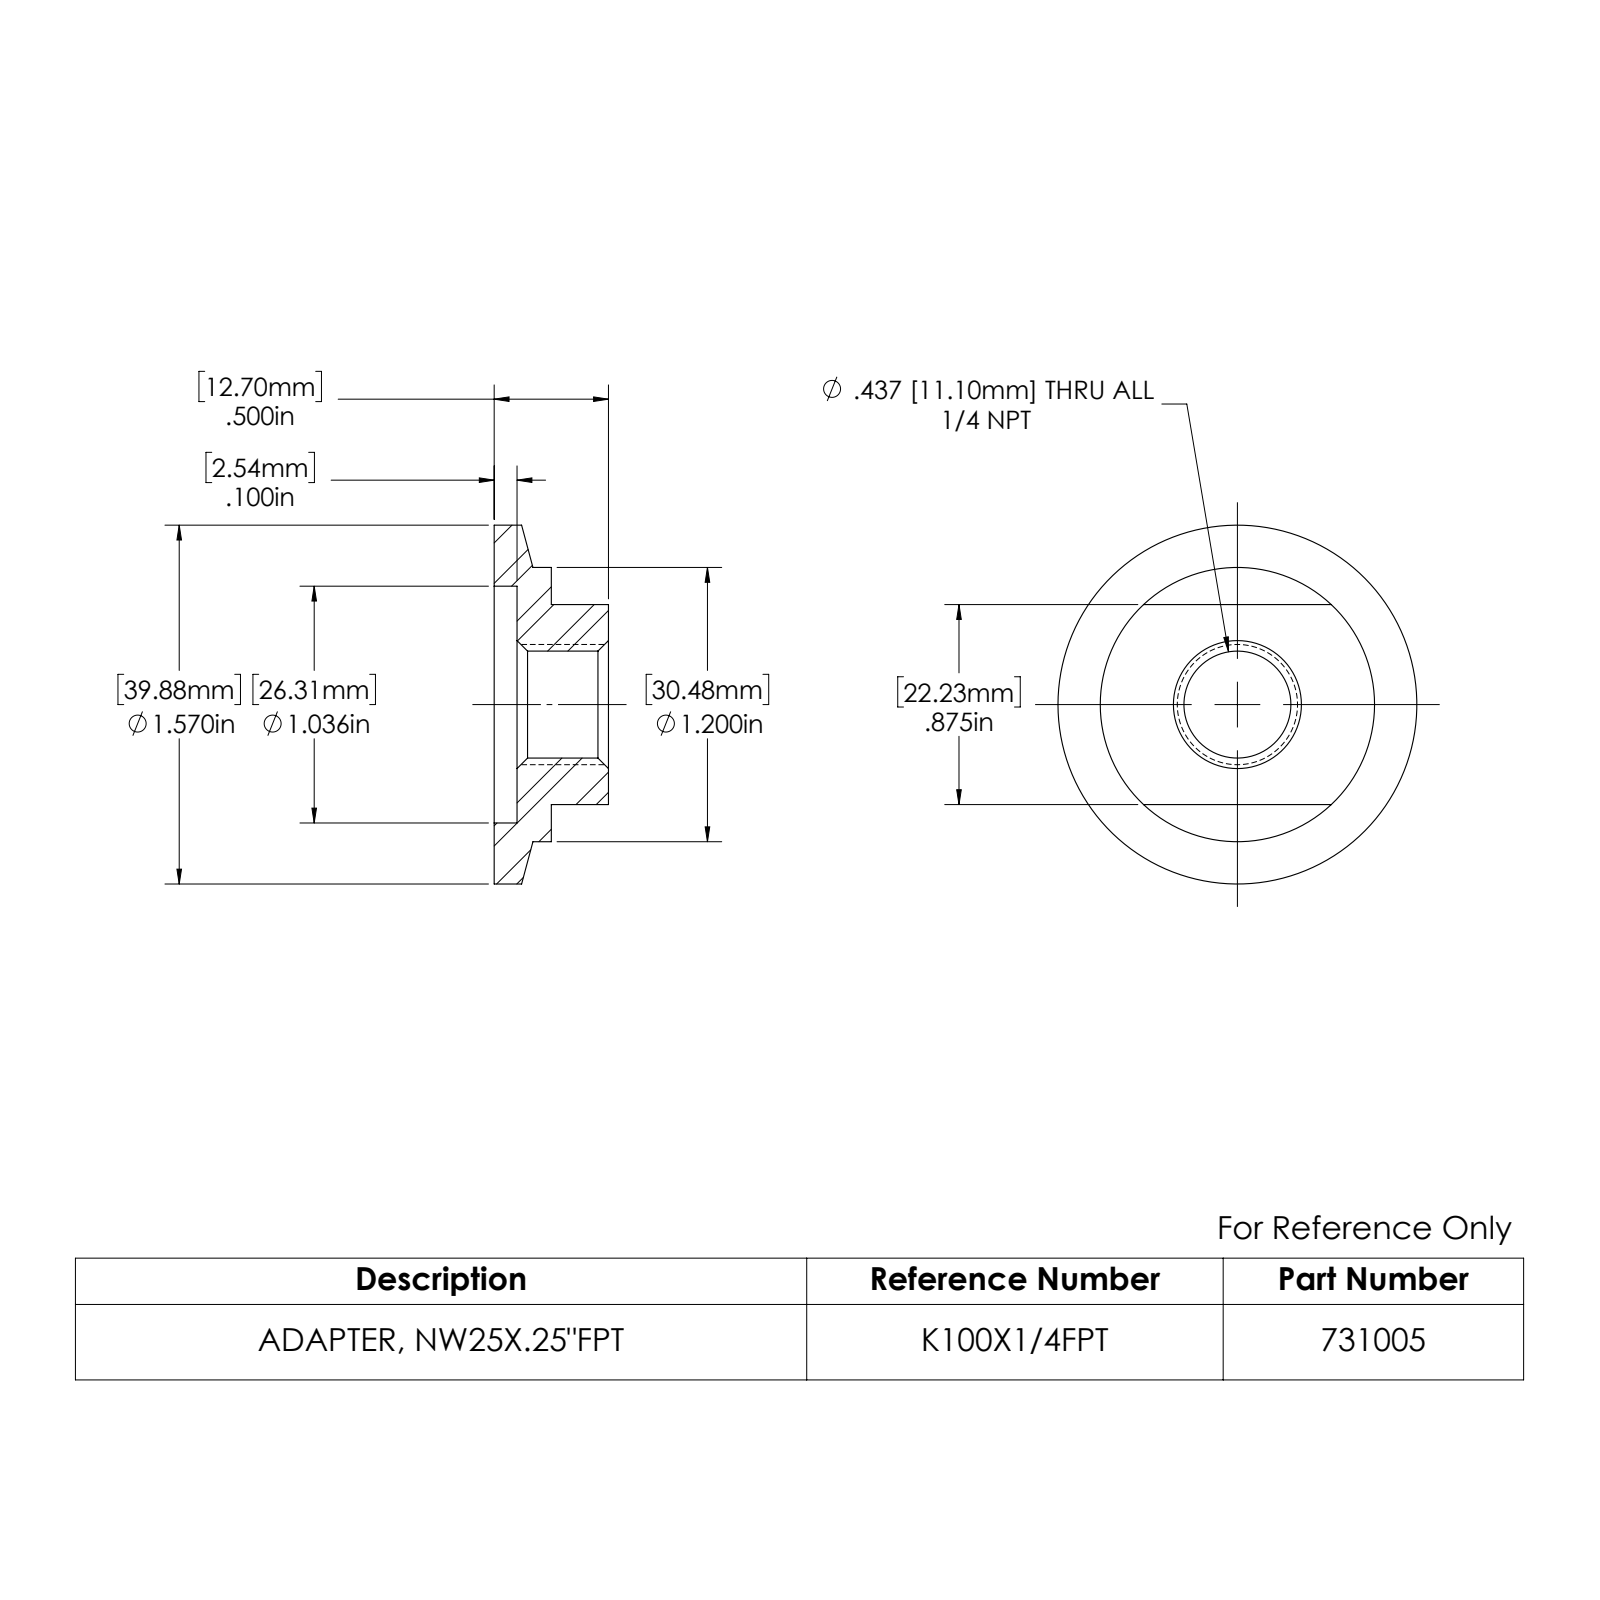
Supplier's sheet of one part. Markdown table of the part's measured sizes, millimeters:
| quantity | value |
| --- | --- |
| part name | 731005 |
| STEP written by | SolidWorks 2022 (AUTOMOTIVE_DESIGN) |
| units | millimeters |
| bodies | 1 solid, 21 faces (7 planar, 8 cylindrical, 6 other) |
| overall size | 39.9 × 39.9 × 12.7 |
| volume | 7 850 mm³ |
| surface area | 3 995 mm² |
| round holes (diameter × count) | 11.9 × 1, 26.3 × 1 |
| round bosses / shafts (diameter × count) | 39.9 × 1, 30.5 × 1 |
| main face-to-face distances | 12.7, 2.5, 10.2, 6.4, 22.2, 3.8 |
